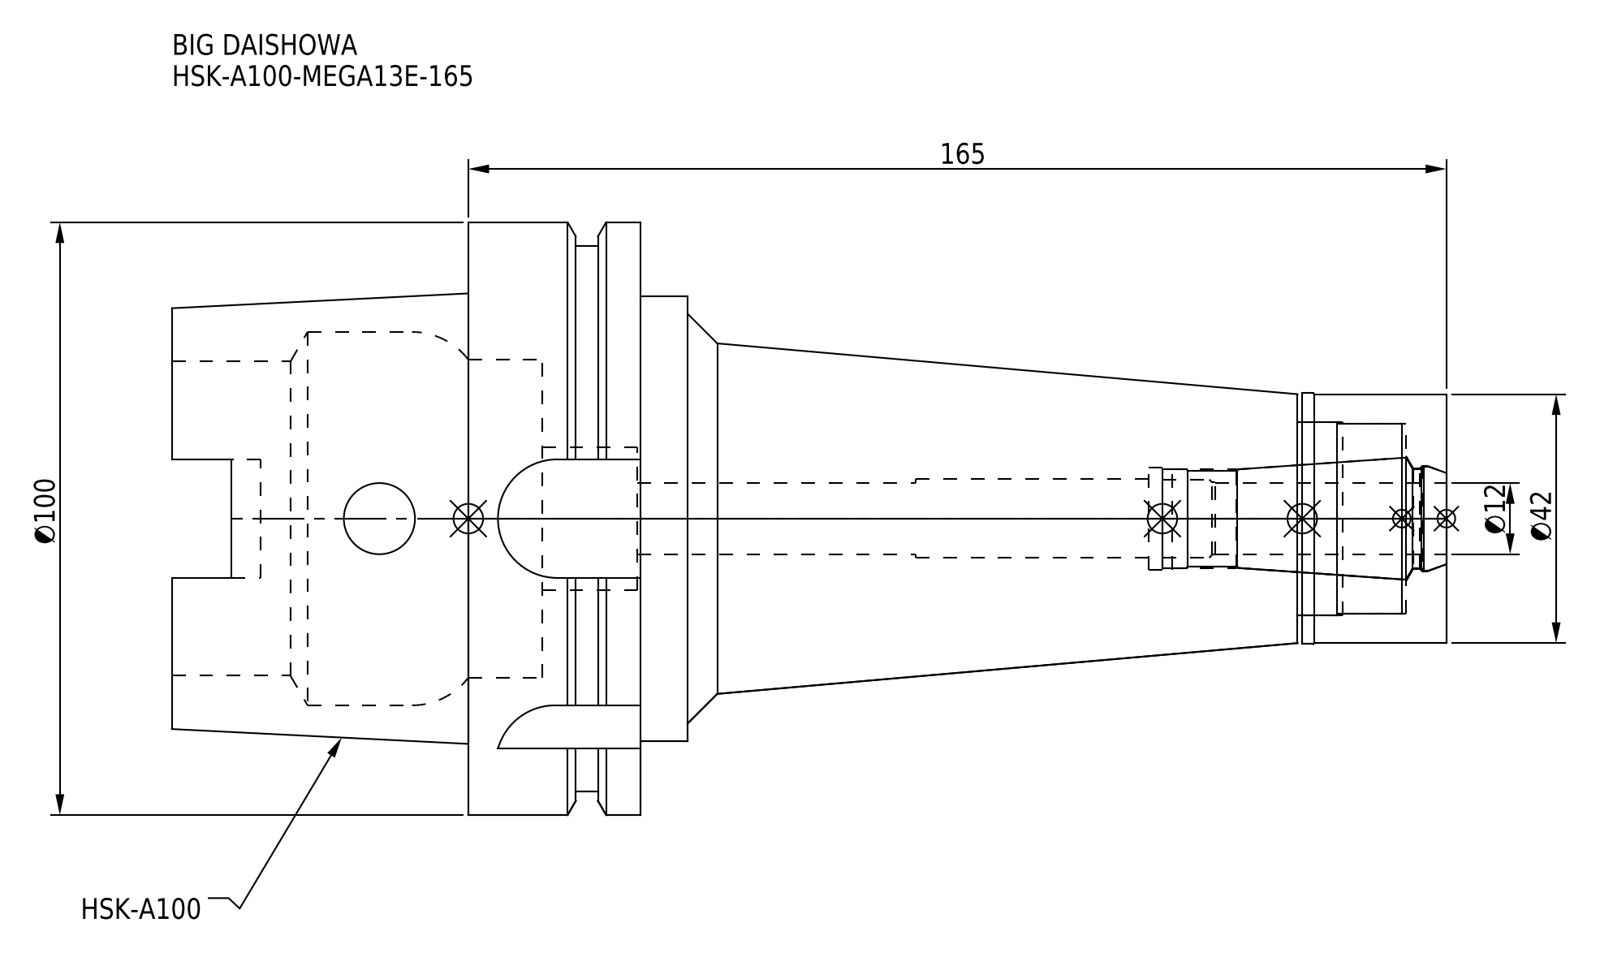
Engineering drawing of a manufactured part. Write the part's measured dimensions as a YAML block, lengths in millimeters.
part_name: "HA100ME13165-120_ASM.stp; HSK-A100-MEGA13E-165_1.stp; MEN13_1.stp; HSK-A100-MEGA13E-165-120.stp (+3 more)"
step_written_by: "SolidWorks 2019 (CONFIG_CONTROL_DESIGN)"
units: millimeters
bodies: {solids: 2, faces: 126, planar: 42, cylindrical: 56, other: 28}
overall_size: [215, 100, 100]
volume: 514180
surface_area: 81551
round_holes:
  - {diameter: 12, count: 2}
  - {diameter: 13.3, count: 1}
  - {diameter: 16.6, count: 1}
  - {diameter: 17, count: 1}
  - {diameter: 17.2, count: 1}
  - {diameter: 17.9, count: 1}
  - {diameter: 24, count: 1}
  - {diameter: 32, count: 1}
  - {diameter: 32.5, count: 1}
  - {diameter: 53, count: 1}
  - {diameter: 53.8, count: 1}
  - {diameter: 63, count: 1}
round_bosses_or_shafts:
  - {diameter: 100, count: 1}
  - {diameter: 92, count: 1}
  - {diameter: 75, count: 1}
  - {diameter: 42.3, count: 1}
  - {diameter: 42, count: 1}
partial_cylinders:
  - {radius: 4.88, count: 4}
  - {radius: 10, count: 4}
face_to_face_distances: [29, 16.55, 12.45, 136, 152.55, 165, 215, 79, 62.45, 50]
